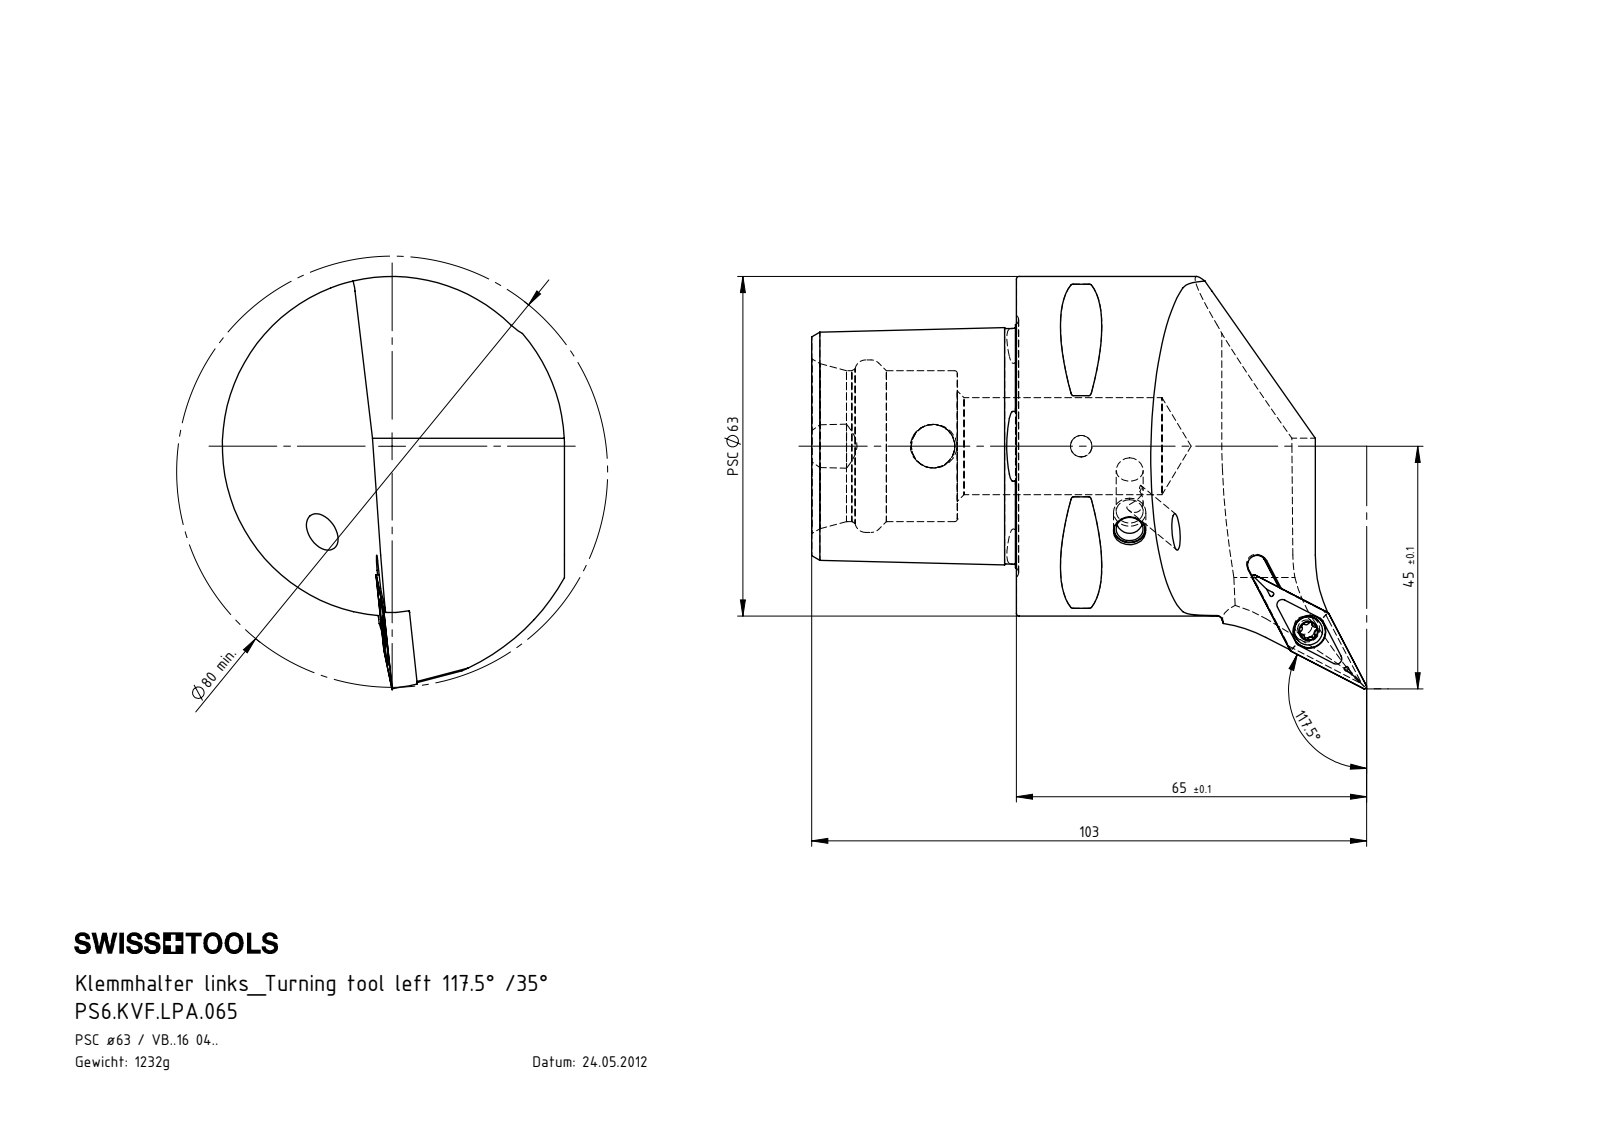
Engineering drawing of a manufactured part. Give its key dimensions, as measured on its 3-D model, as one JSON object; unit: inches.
{"part_name": "PS6.KVF.LPA.065; PS6-KVF.LPA.065_A; WCB-ER2.001.009_A; VBMT160404 (+1 more)", "step_written_by": "SolidWorks 2017 (AUTOMOTIVE_DESIGN)", "units": "inches", "bodies": {"solids": 5, "faces": 204, "planar": 55, "cylindrical": 48, "other": 101}, "overall_size": [4.055, 3.012, 2.5], "volume_in3": 9.434, "surface_area_in2": 42.84, "round_holes": [[0.197, 2], [0.13, 1], [0.157, 1], [0.173, 1], [0.24, 1], [0.319, 1], [0.709, 1], [1.102, 1], [1.26, 1]], "round_bosses_or_shafts": [[2.48, 1], [0.236, 1], [0.207, 1], [0.157, 1]], "partial_cylinders_radius": [[0.02, 8], [0.013, 6], [0.023, 6], [0.006, 2], [0.236, 2], [1.26, 2], [0.069, 1], [0.433, 1]], "face_to_face_distances": [1.496, 0.98, 1.063, 0.433, 2.197, 0.174, 1.488, 0.425, 0.174, 0.187], "hole_center_spacings": [1.083]}
